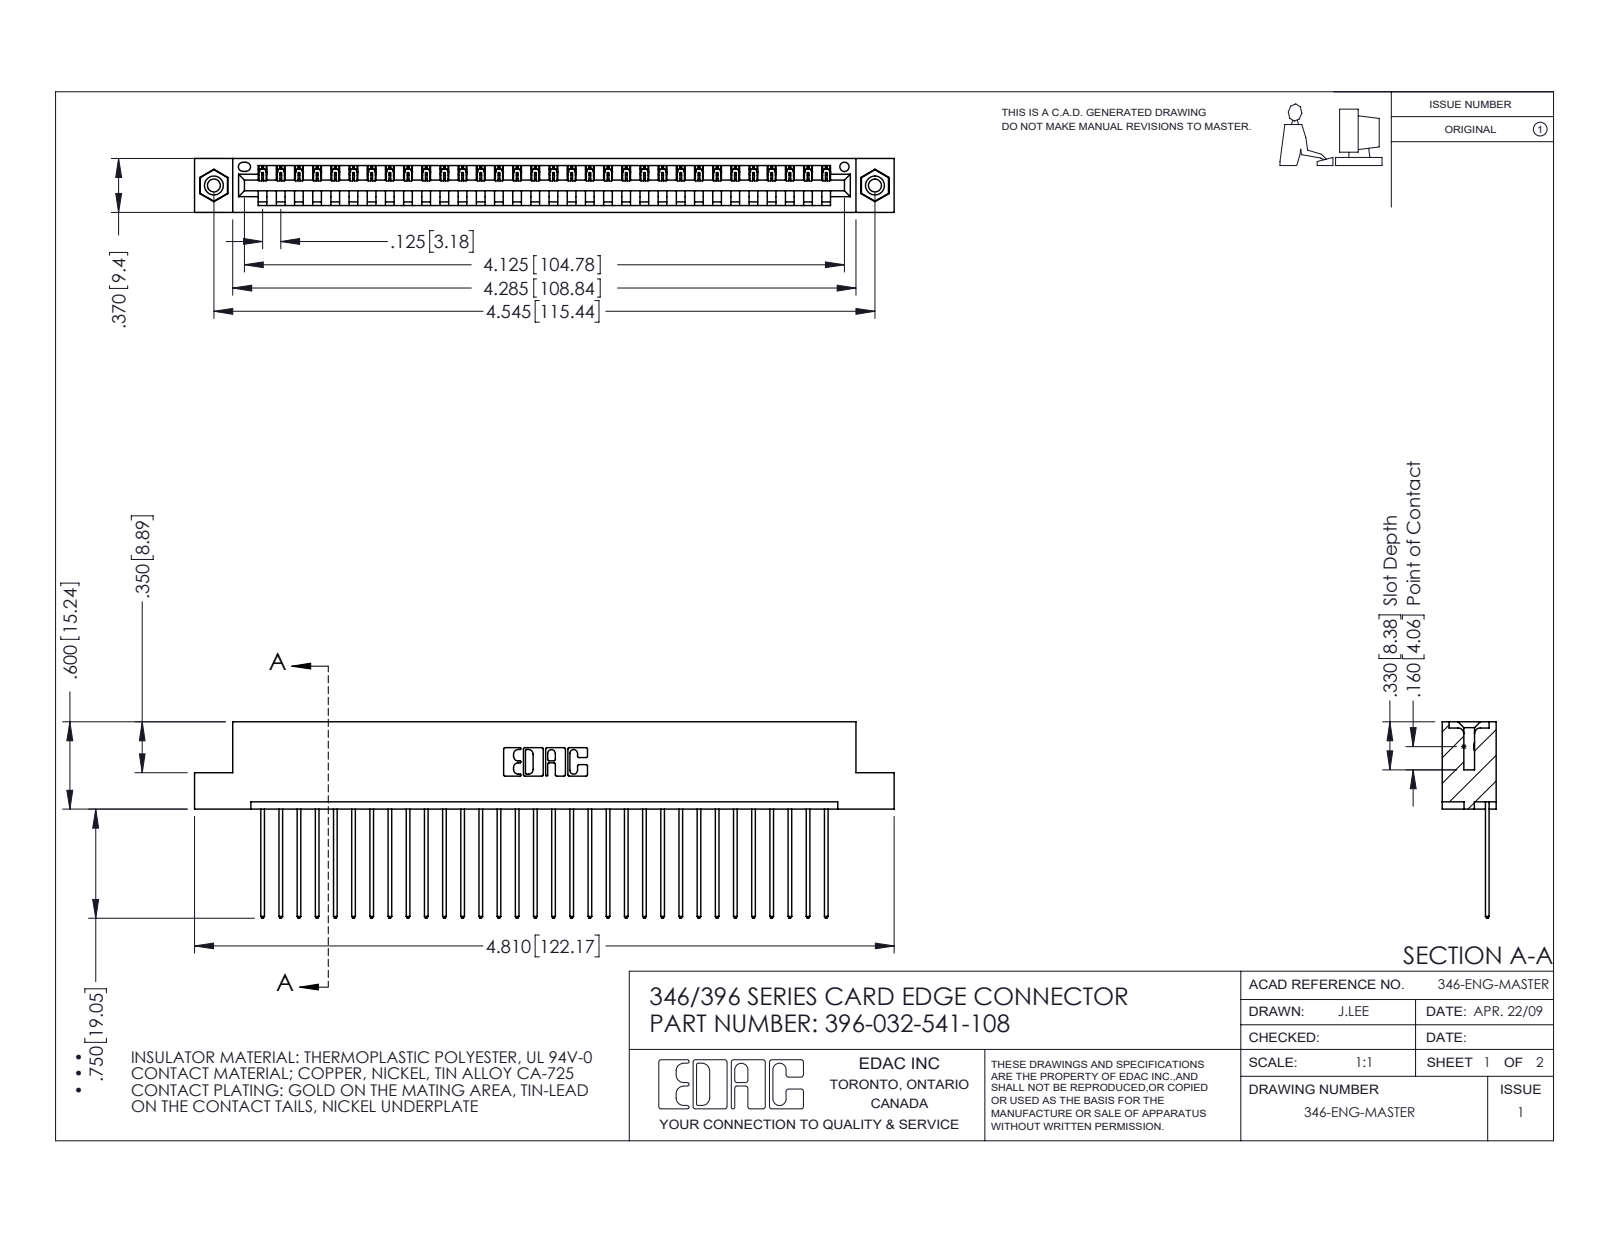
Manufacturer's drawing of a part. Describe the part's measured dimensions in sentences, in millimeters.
The part is named "345-292-001_345-293-141; 346 Part_Flush Mounting Lugs - 0.156 Dia-TI; 345-250-001_345-250-003-102; 396-032-541-108". Its 3-D file was written by "SolidWorks 2016 (CONFIG_CONTROL_DESIGN)". It is 35 solids with 2038 faces: 1388 planar, 634 cylindrical and 16 other. Overall it measures 122.2 by 34.3 by 9.4 millimeters. Its volume is 11 700 cubic millimeters and its surface area 15 200 square millimeters. Round holes: 2 of diameter 2.3, 2 of diameter 3.2, 2 of diameter 4, 1 of diameter 1.6. Round bosses or shafts: 2 of diameter 3.9. Partial cylindrical surfaces (rounded edges, fillets, slot ends): 64 of radius 0.2, 64 of radius 0.3, 22 of radius 0.3, 6 of radius 0.2, 6 of radius 0.8, 3 of radius 0.7, 2 of radius 0.8, 2 of radius 1. The main face-to-face distances are 1.2, 8.2, 9.4, 6.4, 1.8, 7.6, 0.6, 3.8, 5.6, 2.5. The hole center spacings are 6.2, 110.2, 115.4.
